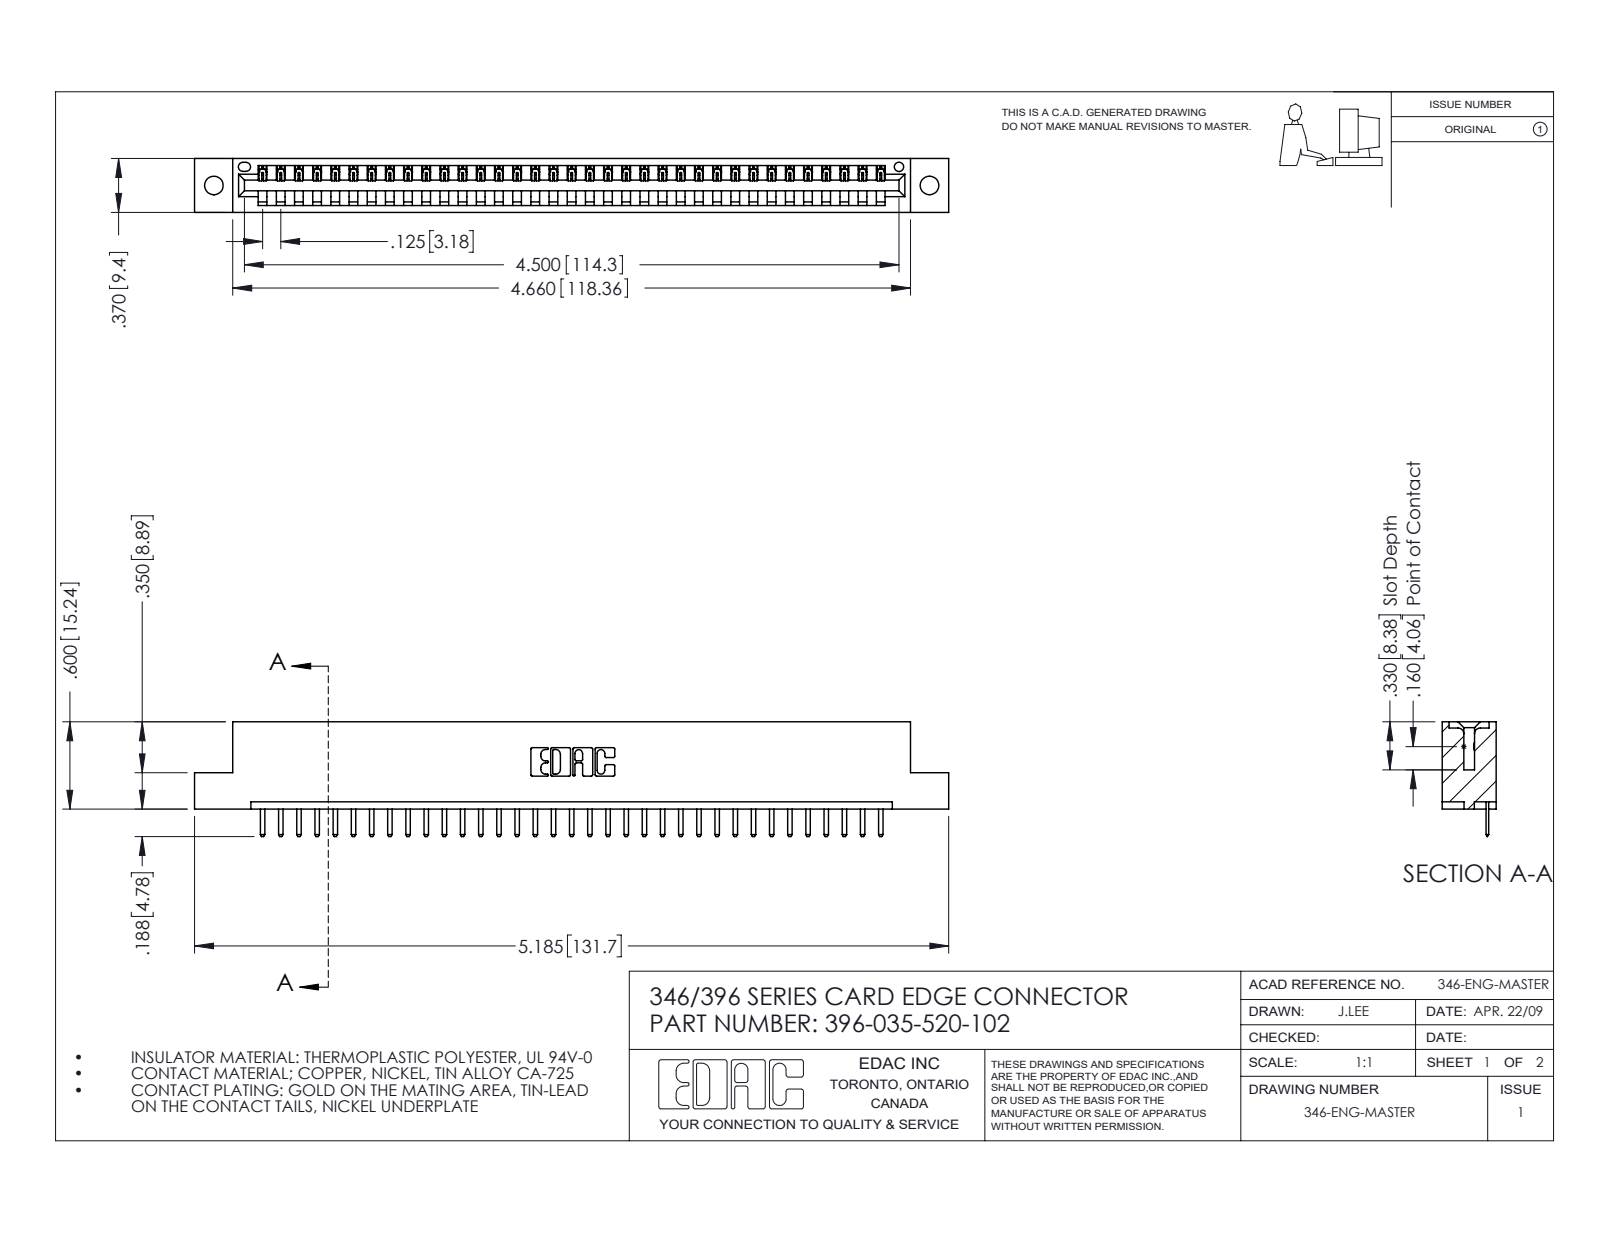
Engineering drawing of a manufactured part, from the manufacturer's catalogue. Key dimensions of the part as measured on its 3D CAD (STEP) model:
Part name (STEP PRODUCT): 345-292-001_345-293-120; 346 Part_Flush Mounting Lugs - 0.128 Dia; 396-035-520-102
STEP written by: SolidWorks 2016 (CONFIG_CONTROL_DESIGN)
Units: inches
Bodies: 36 solids, 2292 faces (1546 planar, 746 cylindrical, 0 other)
Overall size (bounding box): 5.185 × 0.788 × 0.37
Volume: 0.758 in³ · Surface area: 23 in²
Round holes (diameter × count): ⌀0.128 ×2, ⌀0.064 ×1
Partial cylindrical surfaces — rounded edges, fillets, slot ends (radius × count): R0.01 ×72, R0.006 ×70, R0.01 ×22, R0.007 ×6, R0.031 ×6, R0.026 ×3, R0.031 ×2, R0.04 ×2
Main face-to-face distances: 0.048, 0.322, 0.37, 0.25, 0.148, 0.222, 0.1, 0.174, 0.072, 0.298
Hole centre spacings: 0.246, 4.711, 4.92
